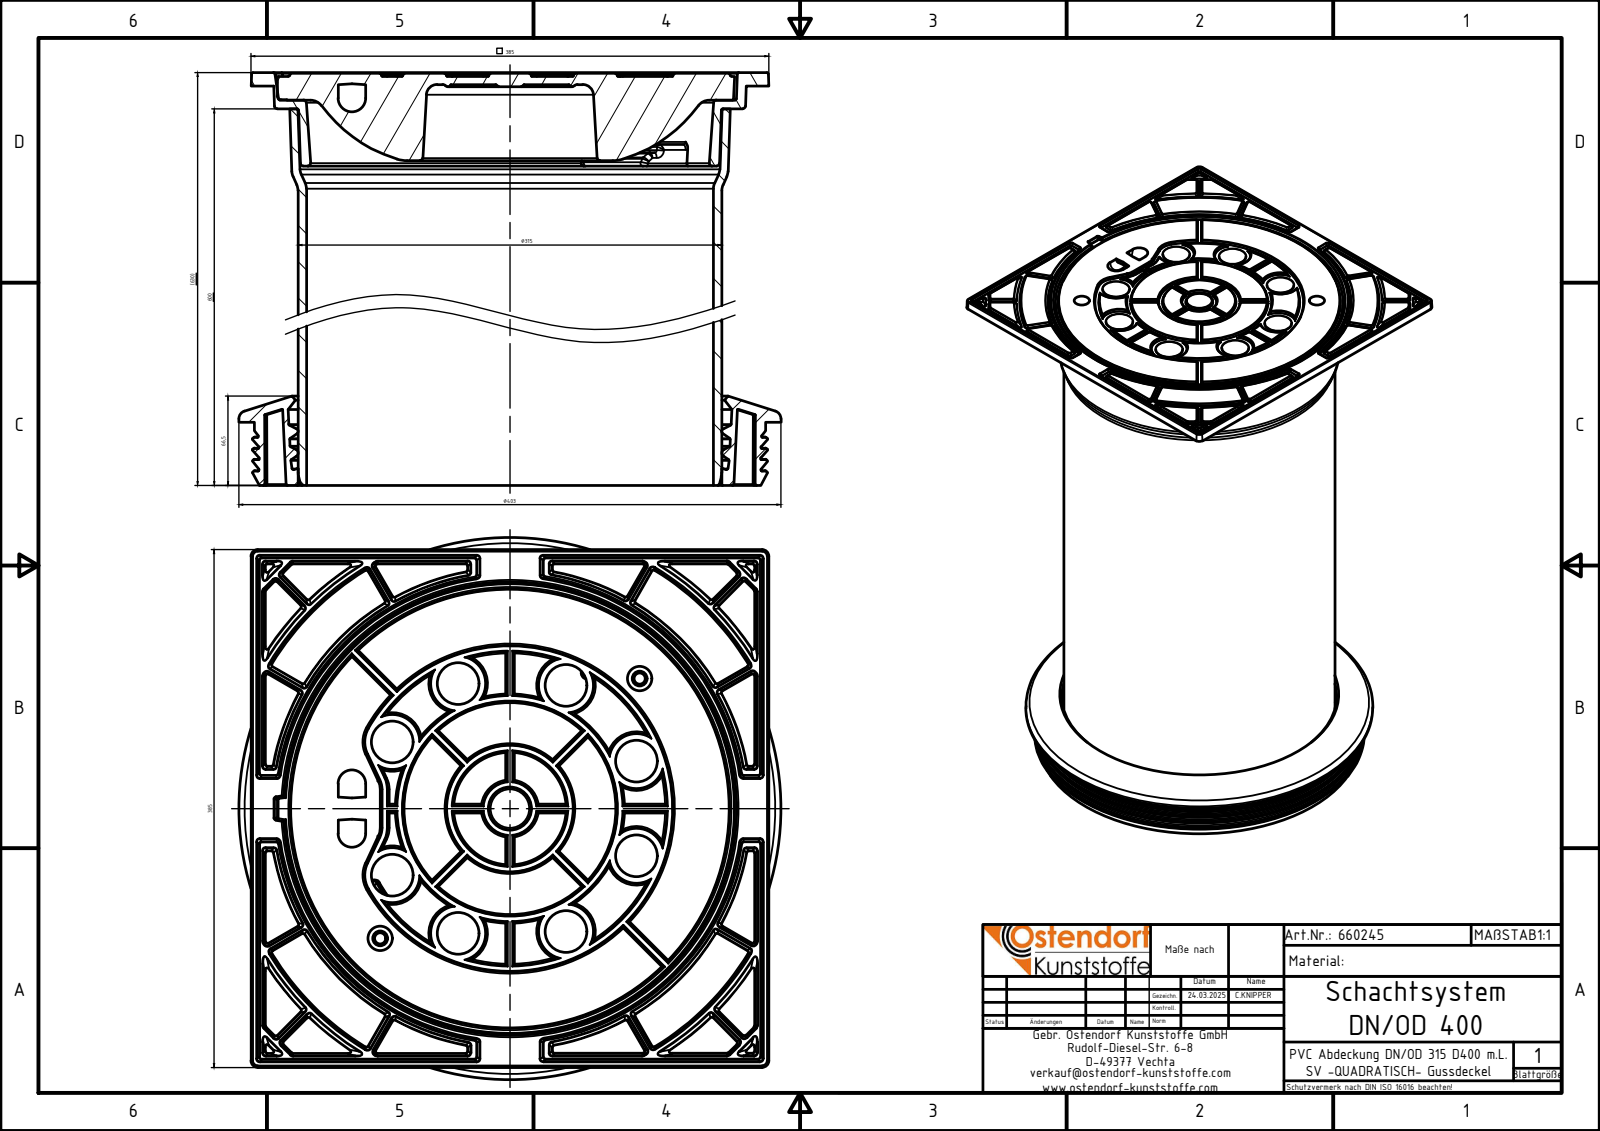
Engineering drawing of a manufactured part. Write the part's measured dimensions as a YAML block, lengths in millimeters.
part_name: "660245z; 660300z; 660500_05.02.25z; 990050z (+1 more)"
step_written_by: "Autodesk Inventor 2024 (AUTOMOTIVE_DESIGN)"
units: millimeters
bodies: {solids: 4, faces: 1838, planar: 245, cylindrical: 371, other: 1222}
overall_size: [627, 403, 403]
volume: 8761000
surface_area: 2157000
round_holes:
  - {diameter: 31, count: 8}
  - {diameter: 8.38, count: 2}
  - {diameter: 11, count: 2}
  - {diameter: 18, count: 2}
  - {diameter: 302.6, count: 1}
  - {diameter: 315, count: 1}
round_bosses_or_shafts:
  - {diameter: 403, count: 1}
  - {diameter: 380, count: 1}
partial_cylinders:
  - {radius: 1, count: 208}
  - {radius: 2.5, count: 48}
  - {radius: 0.5, count: 18}
  - {radius: 4, count: 8}
  - {radius: 2, count: 4}
  - {radius: 3, count: 1}
face_to_face_distances: [9.5, 0.5, 10, 10.5, 20.5, 20, 6.5, 17, 26.5, 27]
hole_center_spacings: [100.5, 65.44, 76.92, 80.14, 100.49, 135.79, 137.08, 144.58]
